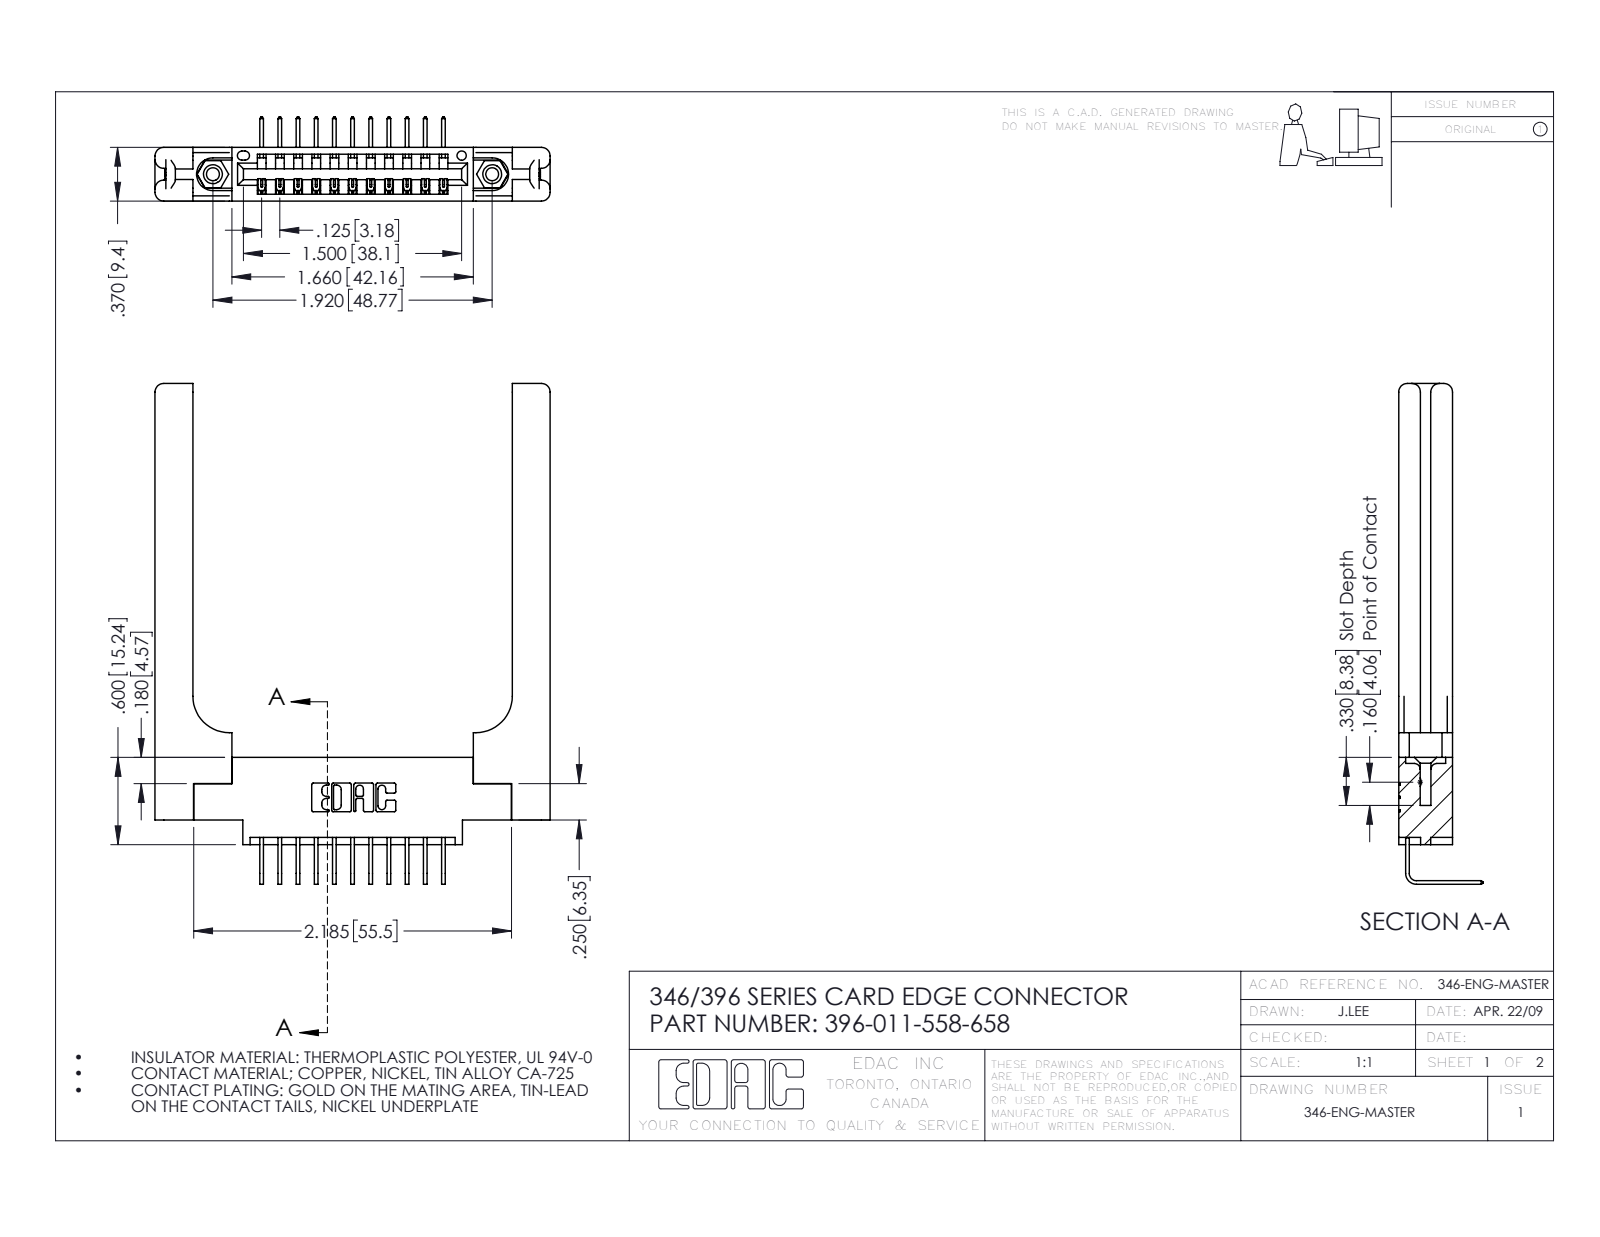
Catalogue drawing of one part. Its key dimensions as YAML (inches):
part_name: "346-220-058_345-220-058; 345-250-001_345-250-001-102; 396-011-558-658; 345-292-001_558 Tail - 2 (+1 more)"
step_written_by: "SolidWorks 2016 (CONFIG_CONTROL_DESIGN)"
units: inches
bodies: {solids: 16, faces: 1042, planar: 690, cylindrical: 292, other: 60}
overall_size: [3.443, 2.716, 0.58]
volume: 0.842
surface_area: 20.23
round_holes:
  - {diameter: 0.089, count: 2}
  - {diameter: 0.125, count: 2}
  - {diameter: 0.156, count: 2}
  - {diameter: 0.064, count: 1}
round_bosses_or_shafts:
  - {diameter: 0.155, count: 2}
partial_cylinders:
  - {radius: 0.006, count: 22}
  - {radius: 0.01, count: 22}
  - {radius: 0.06, count: 16}
  - {radius: 0.007, count: 6}
  - {radius: 0.031, count: 6}
  - {radius: 0.026, count: 3}
  - {radius: 0.03, count: 2}
  - {radius: 0.031, count: 2}
face_to_face_distances: [0.37, 0.15, 0.072, 0.148, 0.22, 0.322, 0.048, 0.25, 0.102, 0.173]
hole_center_spacings: [0.246, 1.715, 1.92]
